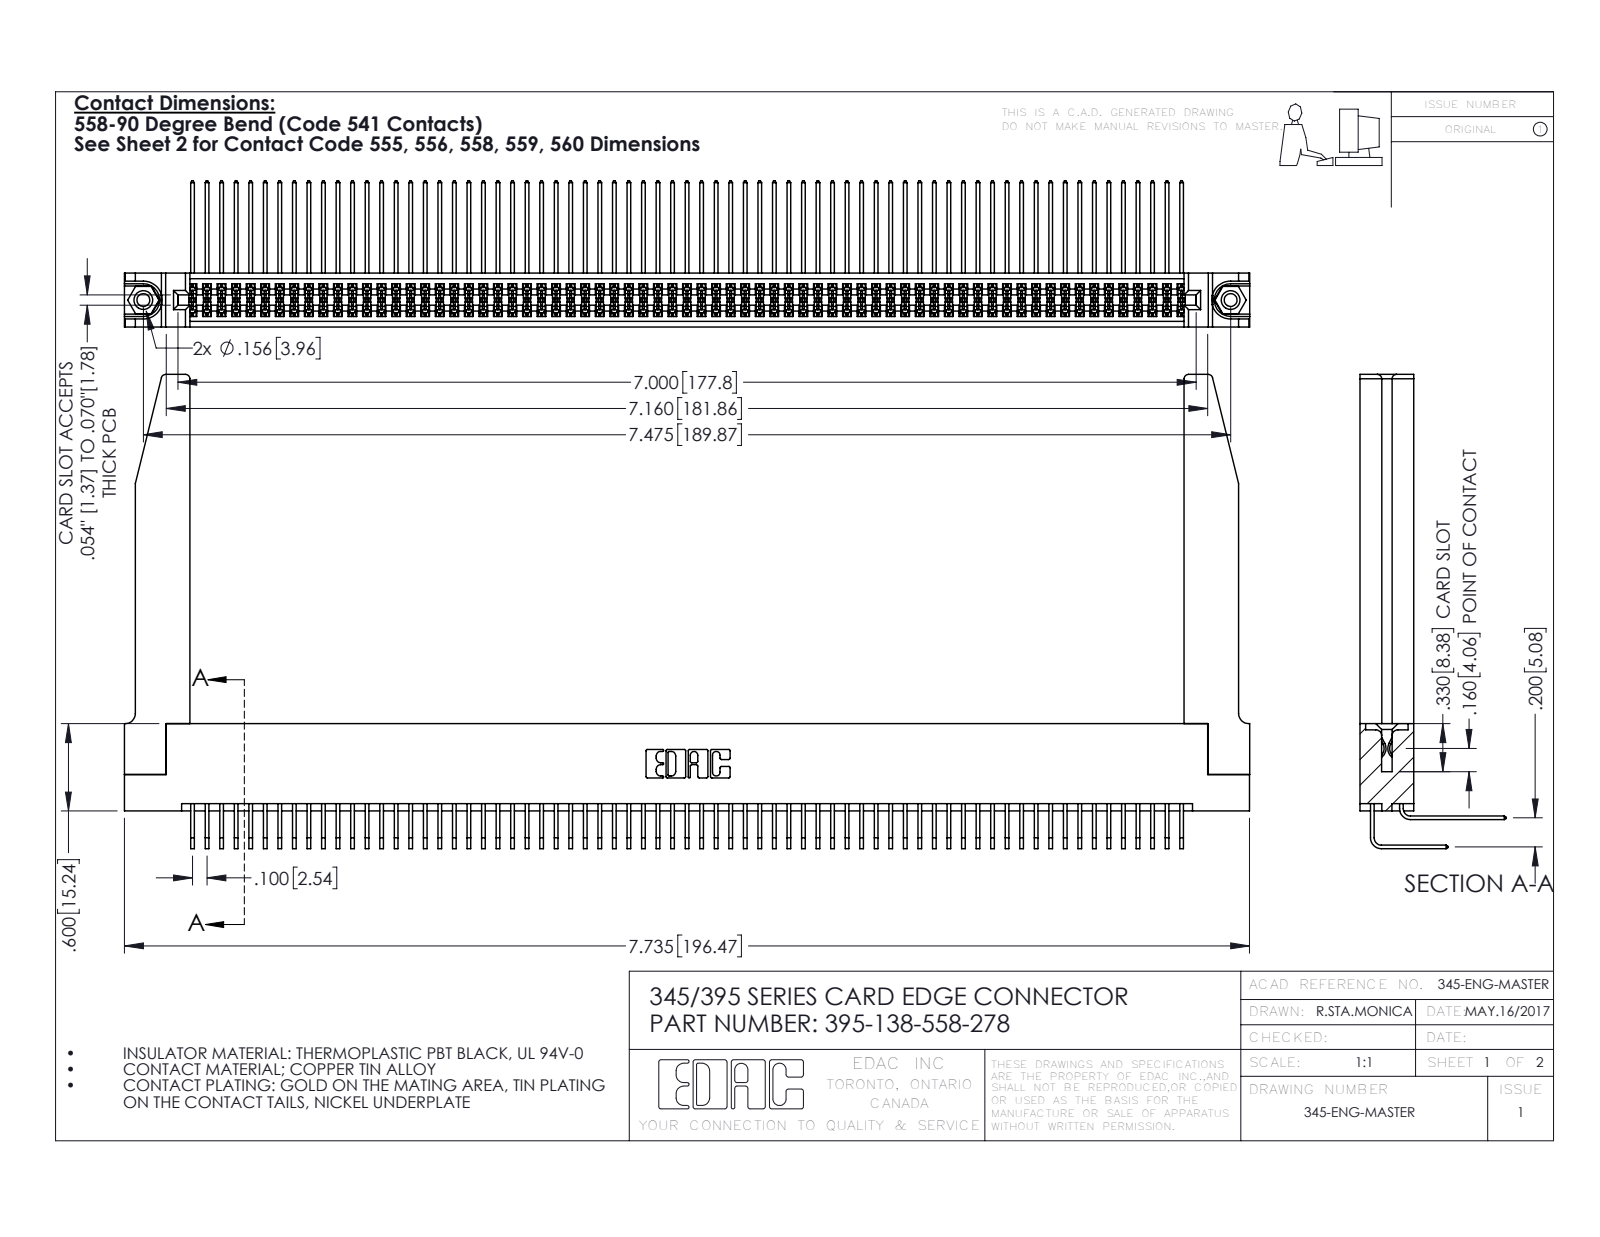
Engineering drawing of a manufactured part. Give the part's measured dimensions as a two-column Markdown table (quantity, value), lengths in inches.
| quantity | value |
| --- | --- |
| part name | 345-250-001_345-250-001-102; 345 Part_Flush Mounting Lugs - 0.156 Dia-TH; 345-292-001_558 559 Tail - 1; 345-292-001_558 Tail - 2 (+2 more) |
| STEP written by | SolidWorks 2016 (CONFIG_CONTROL_DESIGN) |
| units | inches |
| bodies | 143 solids, 7536 faces (5052 planar, 2432 cylindrical, 52 other) |
| overall size | 7.736 × 3.259 × 1.005 |
| volume | 1.703 in³ |
| surface area | 63.34 in² |
| round holes (diameter × count) | 0.089 × 2, 0.125 × 2, 0.156 × 2, 0.064 × 1 |
| round bosses / shafts (diameter × count) | 0.155 × 2 |
| partial cylindrical surfaces (radius × count) | 0.006 × 275, 0.01 × 22, 0.03 × 8, 0.007 × 6, 0.031 × 6, 0.026 × 3, 0.014 × 2, 0.019 × 2 |
| main face-to-face distances | 0.072, 0.298, 0.37, 0.2, 0.098, 0.272, 0.025, 0.225, 0.025, 0.175 |
| hole center spacings | 0.27, 7.239, 7.475 |
